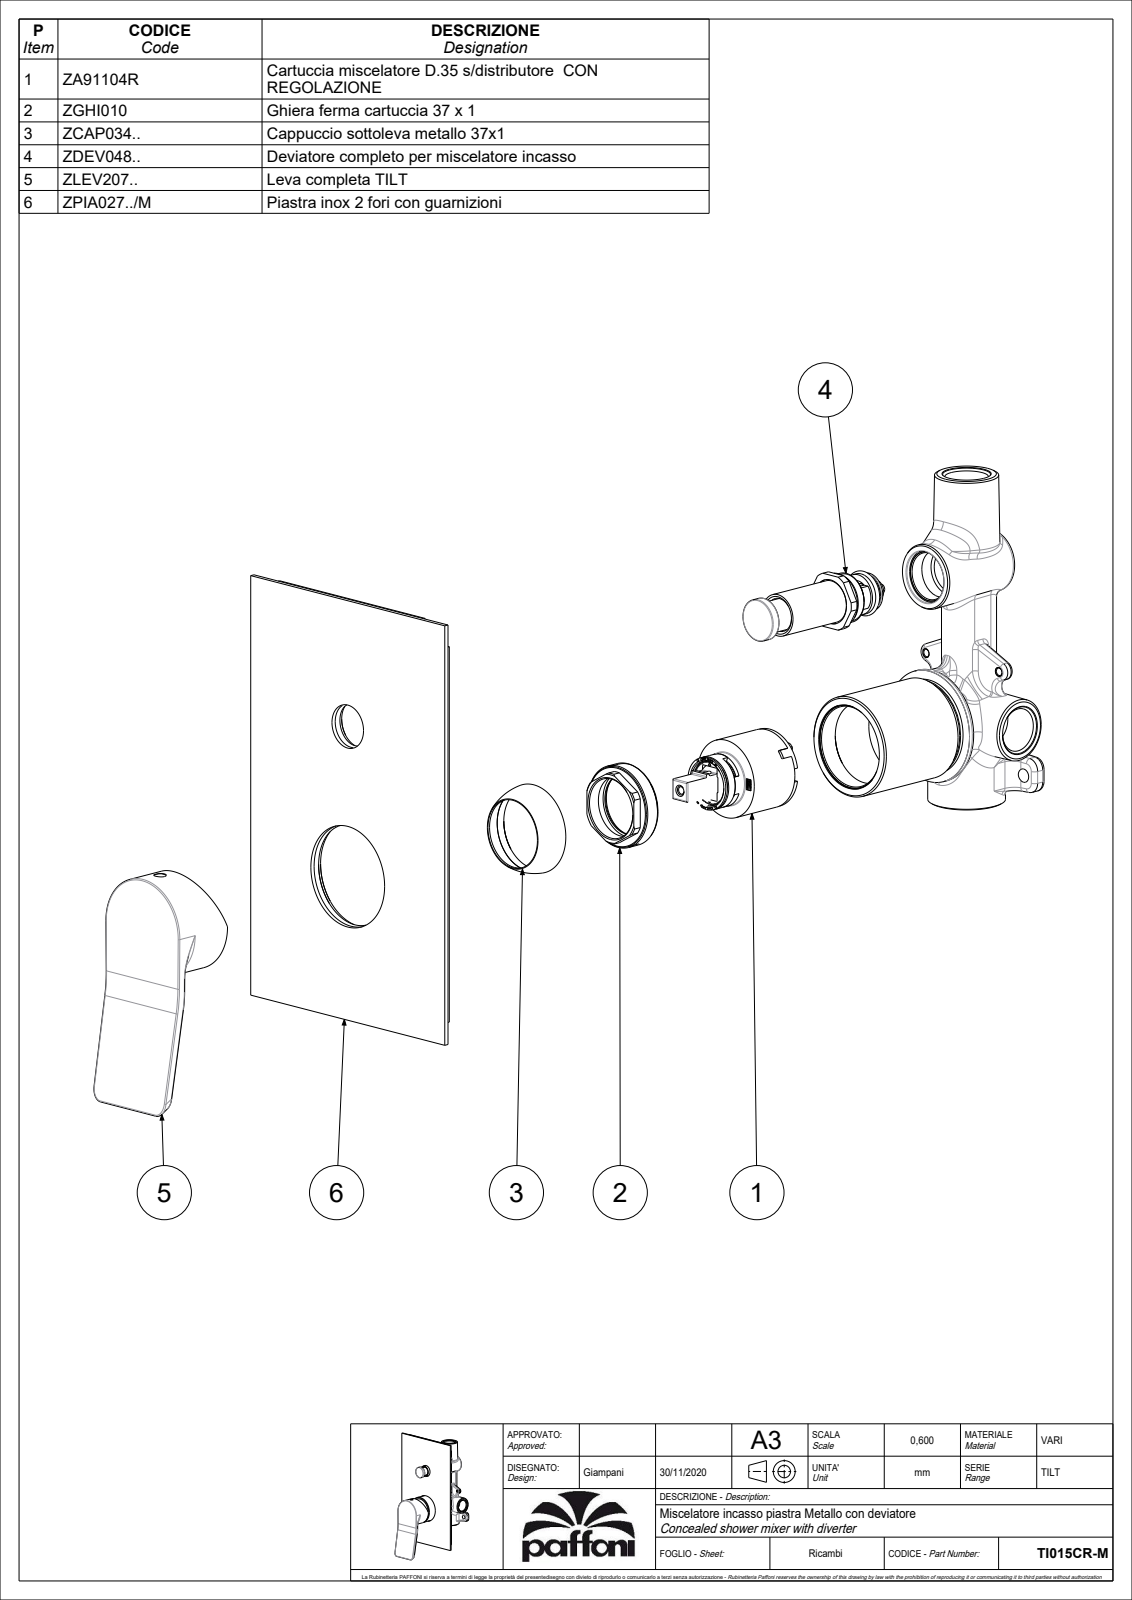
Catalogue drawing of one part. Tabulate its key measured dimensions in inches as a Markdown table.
| quantity | value |
| --- | --- |
| part name | TI015CR-M |
| STEP written by | CREO PARAMETRIC BY PTC INC, 2020044 (CONFIG_CONTROL_DESIGN) |
| units | inches |
| bodies | 0 solids, 75 faces (21 planar, 26 cylindrical, 28 other) |
| overall size | 8.054 × 4.724 × 2.285 |
| round bosses / shafts (diameter × count) | 1.791 × 1, 1.764 × 1, 0.736 × 1, 0.732 × 1, 0.551 × 1, 0.299 × 1 |
| partial cylindrical surfaces (radius × count) | 0.02 × 10, 0.197 × 2, 1.738 × 1, 2.48 × 1 |
| main face-to-face distances | 0.079, 0.158, 1.933, 1.854, 0.669, 0.591, 1.264, 4.724, 0.157, 1.697 |
